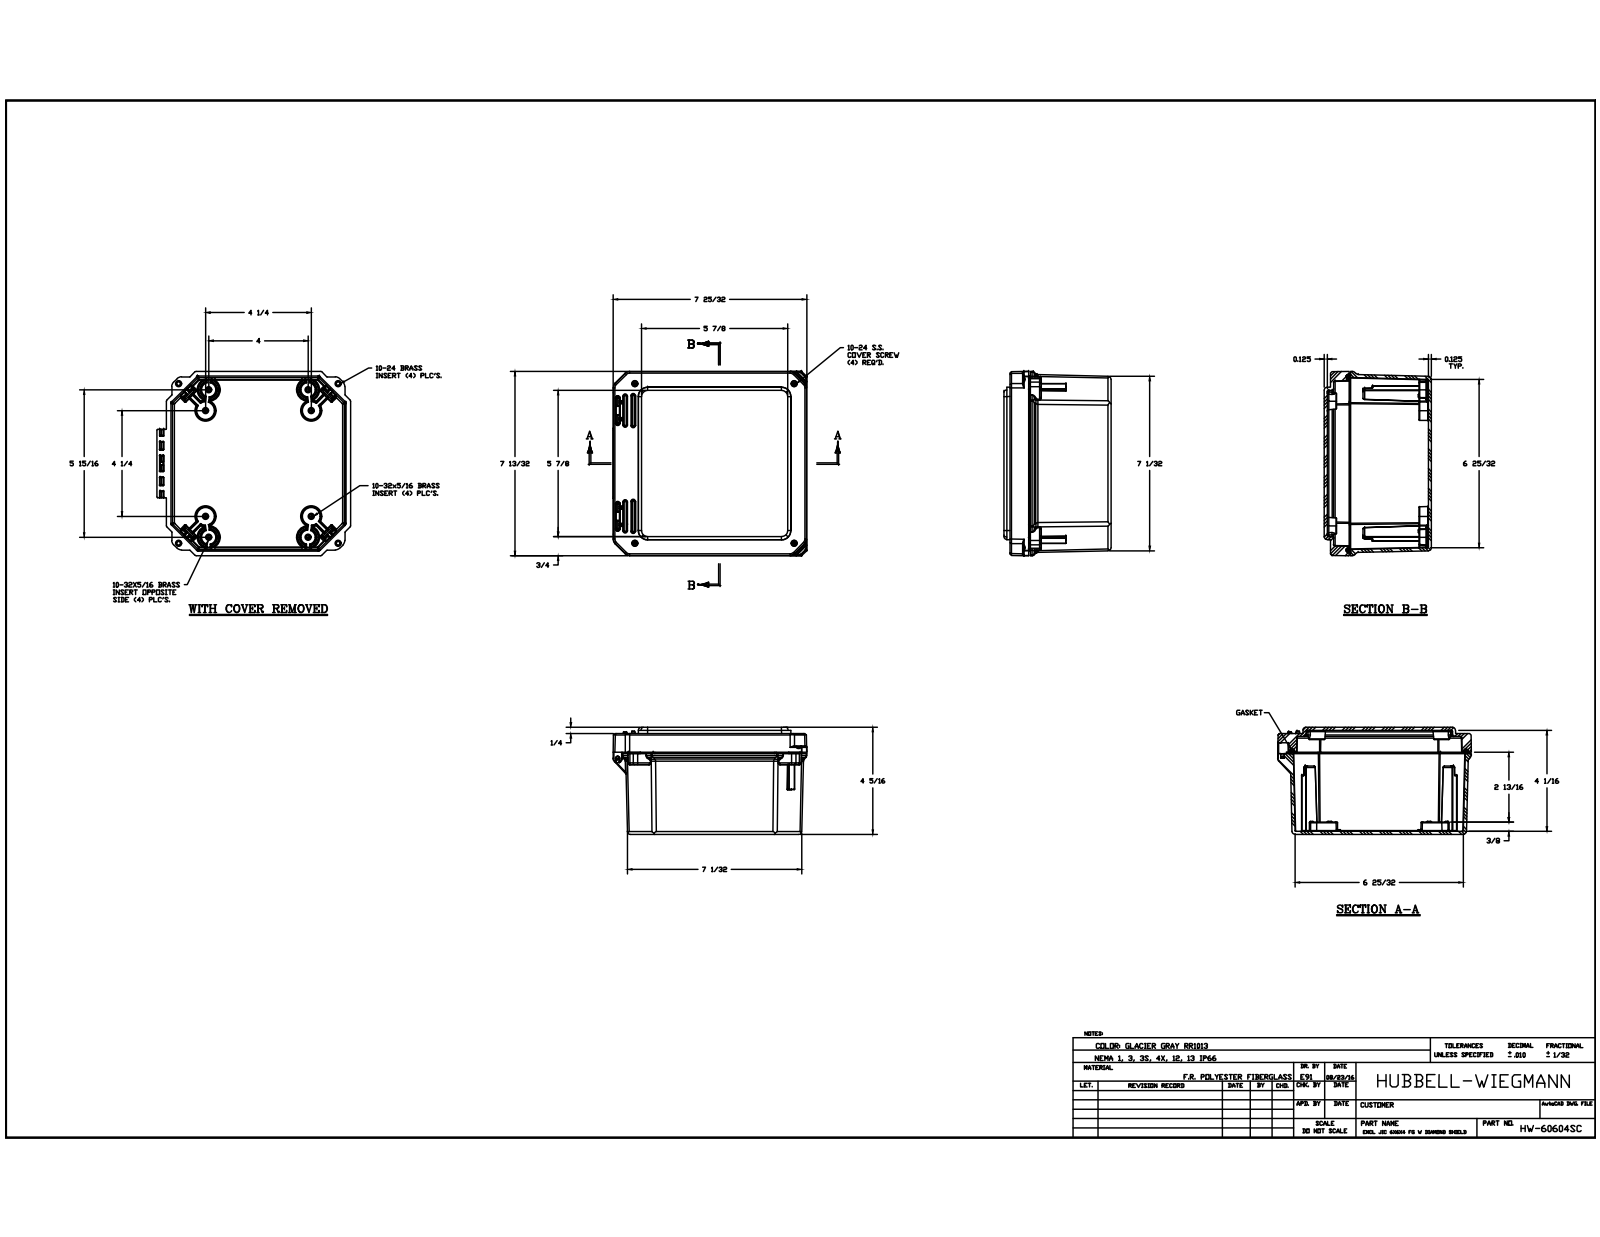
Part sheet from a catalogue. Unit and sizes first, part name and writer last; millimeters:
Units: millimetres
Overall size (bounding box): 197.87 × 188.39 × 109.48
Round holes (diameter × count): ⌀3.96 ×12, ⌀3.86 ×8, ⌀6.4 ×4, ⌀6.43 ×4, ⌀5.56 ×2, ⌀5.77 ×2, ⌀7.94 ×2, ⌀3.48 ×1
Round bosses / shafts (diameter × count): ⌀6.25 ×12, ⌀22.1 ×4, ⌀11.43 ×4, ⌀5.05 ×4, ⌀11.05 ×2
Partial cylindrical surfaces — rounded edges, fillets, slot ends (radius × count): R0.25 ×109, R0.13 ×80, R0.51 ×63, R0.76 ×45, R1.59 ×28, R0.76 ×24, R2.29 ×24, R2.44 ×22
Main face-to-face distances: 3.17, 106.31, 109.48, 103.14, 6.35, 3.15, 3.18, 99.96, 9.53, 103.13
Hole centre spacings: 138.19, 31.27, 146.28, 21.57, 38.88, 106.92, 107.94, 127.46
Volume: 618 284 mm³ · Surface area: 322 753 mm²
Bodies: 23 solids, 1977 faces (648 planar, 709 cylindrical, 620 other)
Part name (STEP PRODUCT): DS60604W_STP; DS060604BOX; BRASS INSERT-(; BRASS INSERT-(_1 (+5 more)
STEP written by: Autodesk Inventor 2017 (CONFIG_CONTROL_DESIGN)
